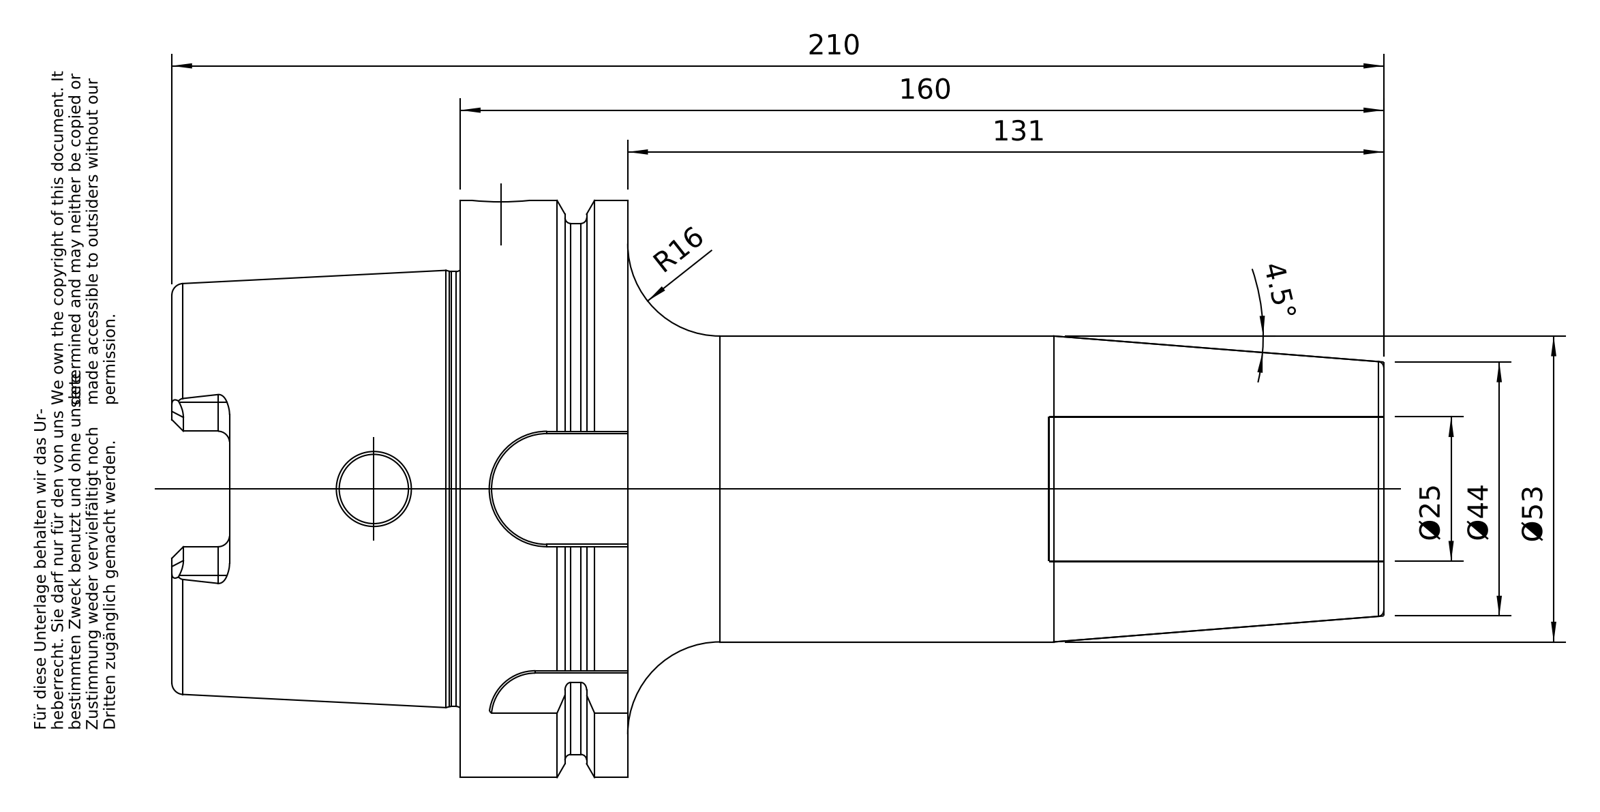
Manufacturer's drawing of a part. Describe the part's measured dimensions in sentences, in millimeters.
The part is named "A100-142-25". Its 3-D file was written by "PRO/ENGINEER BY PARAMETRIC TECHNOLOGY CORPORATION, 2010430 (CONFIG_CONTROL_DESIGN)". It is 1 solid with 174 faces: 50 planar, 51 cylindrical and 73 other. Overall it measures 210 by 100 by 100 millimeters. Its volume is 504 898 cubic millimeters and its surface area 74 058 square millimeters. Round holes: 1 of diameter 10, 1 of diameter 12, 1 of diameter 22.5, 1 of diameter 24, 1 of diameter 24.32, 1 of diameter 24.5, 1 of diameter 25, 1 of diameter 53, 1 of diameter 63. Round bosses or shafts: 1 of diameter 100, 1 of diameter 92, 1 of diameter 75.36. Partial cylindrical surfaces (rounded edges, fillets, slot ends): 6 of radius 2, 4 of radius 5, 1 of radius 8, 1 of radius 10, 1 of radius 11. The main face-to-face distances are 29, 12.5, 16.5, 160, 147.5, 131, 50, 62.5, 79, 210.
